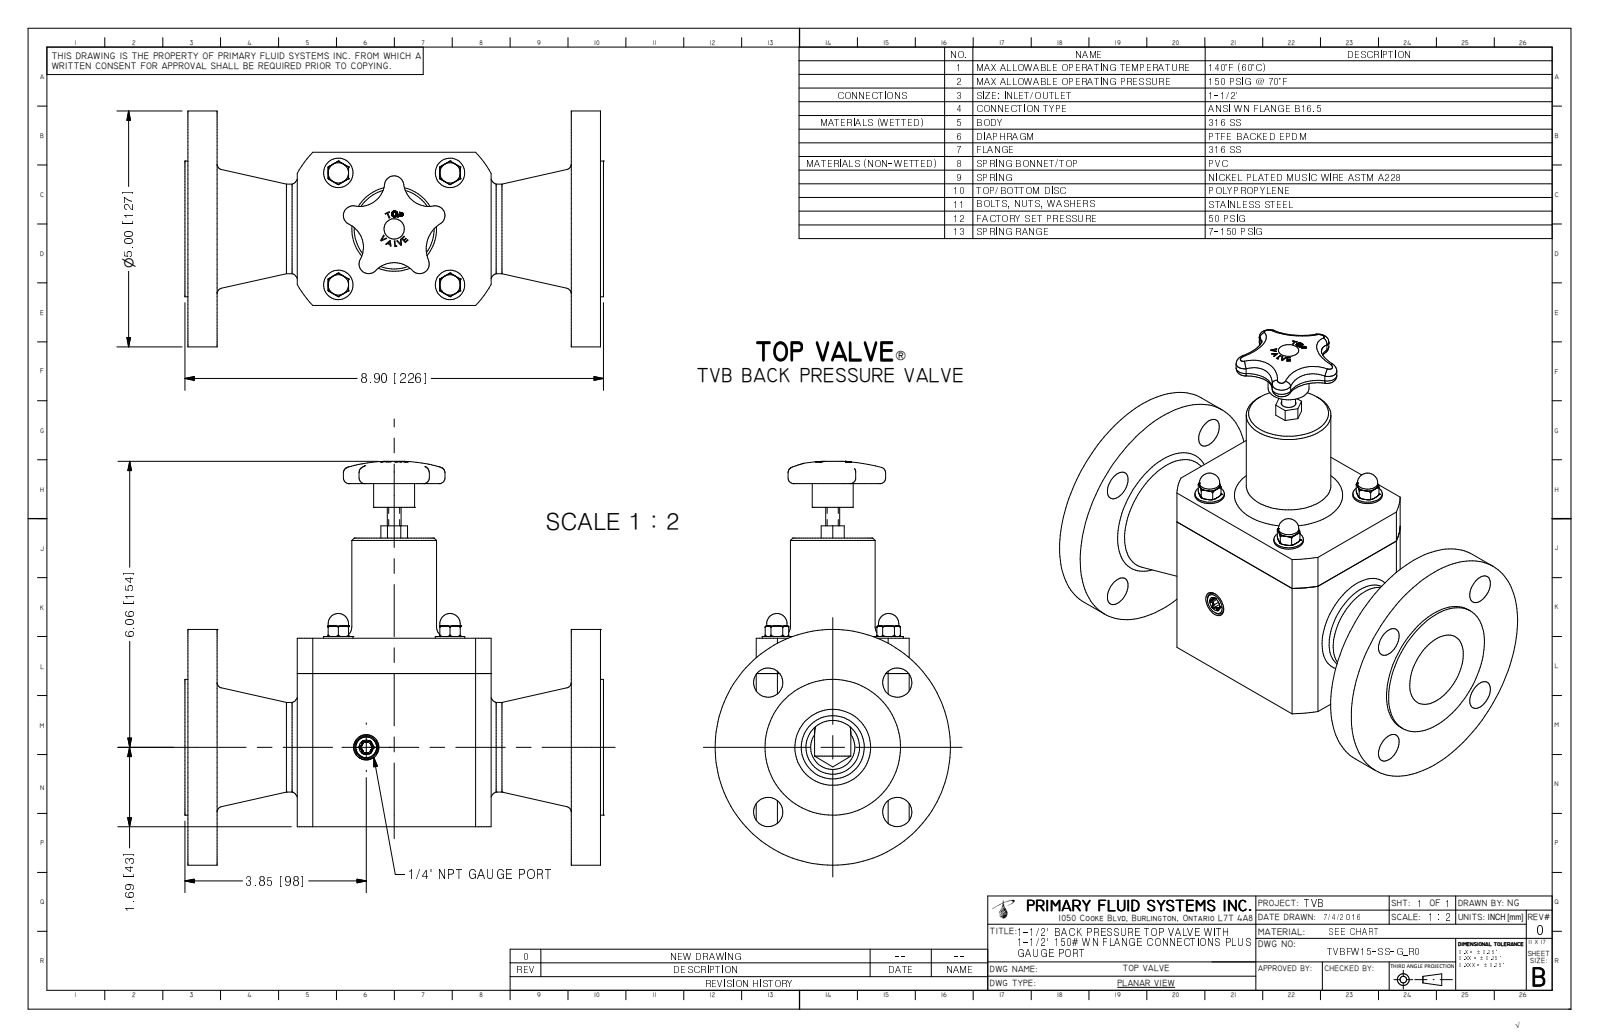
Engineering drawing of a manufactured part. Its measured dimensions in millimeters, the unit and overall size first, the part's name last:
Units: millimetres
Overall size (bounding box): 225.9 × 217.6 × 127
Round holes (diameter × count): ⌀4.4 ×4, ⌀15.7 ×4, ⌀40.9 ×1
Round bosses / shafts (diameter × count): ⌀15.9 ×4, ⌀11 ×4, ⌀9.5 ×4, ⌀127 ×1, ⌀73.2 ×1, ⌀48.3 ×1, ⌀45.7 ×1, ⌀22.1 ×1
Partial cylindrical surfaces — rounded edges, fillets, slot ends (radius × count): R0.7 ×6, R2.2 ×5, R5.2 ×5, R13.6 ×4, R16.7 ×4, R15.9 ×1, R18.9 ×1, R60.3 ×1
Main face-to-face distances: 15.7, 207, 82.6, 191.3, 222.8, 59, 163.8, 43.2, 148, 1.6
Hole centre spacings: 49.3, 69.7, 60.3, 60.3, 85.3, 98.6
Volume: 1 371 000 mm³ · Surface area: 162 100 mm²
Bodies: 1 solid, 383 faces (158 planar, 65 cylindrical, 160 other)
Part name (STEP PRODUCT): TVBFW15-SS-G-R0
STEP written by: Autodesk Inventor 2009 (AUTOMOTIVE_DESIGN)
